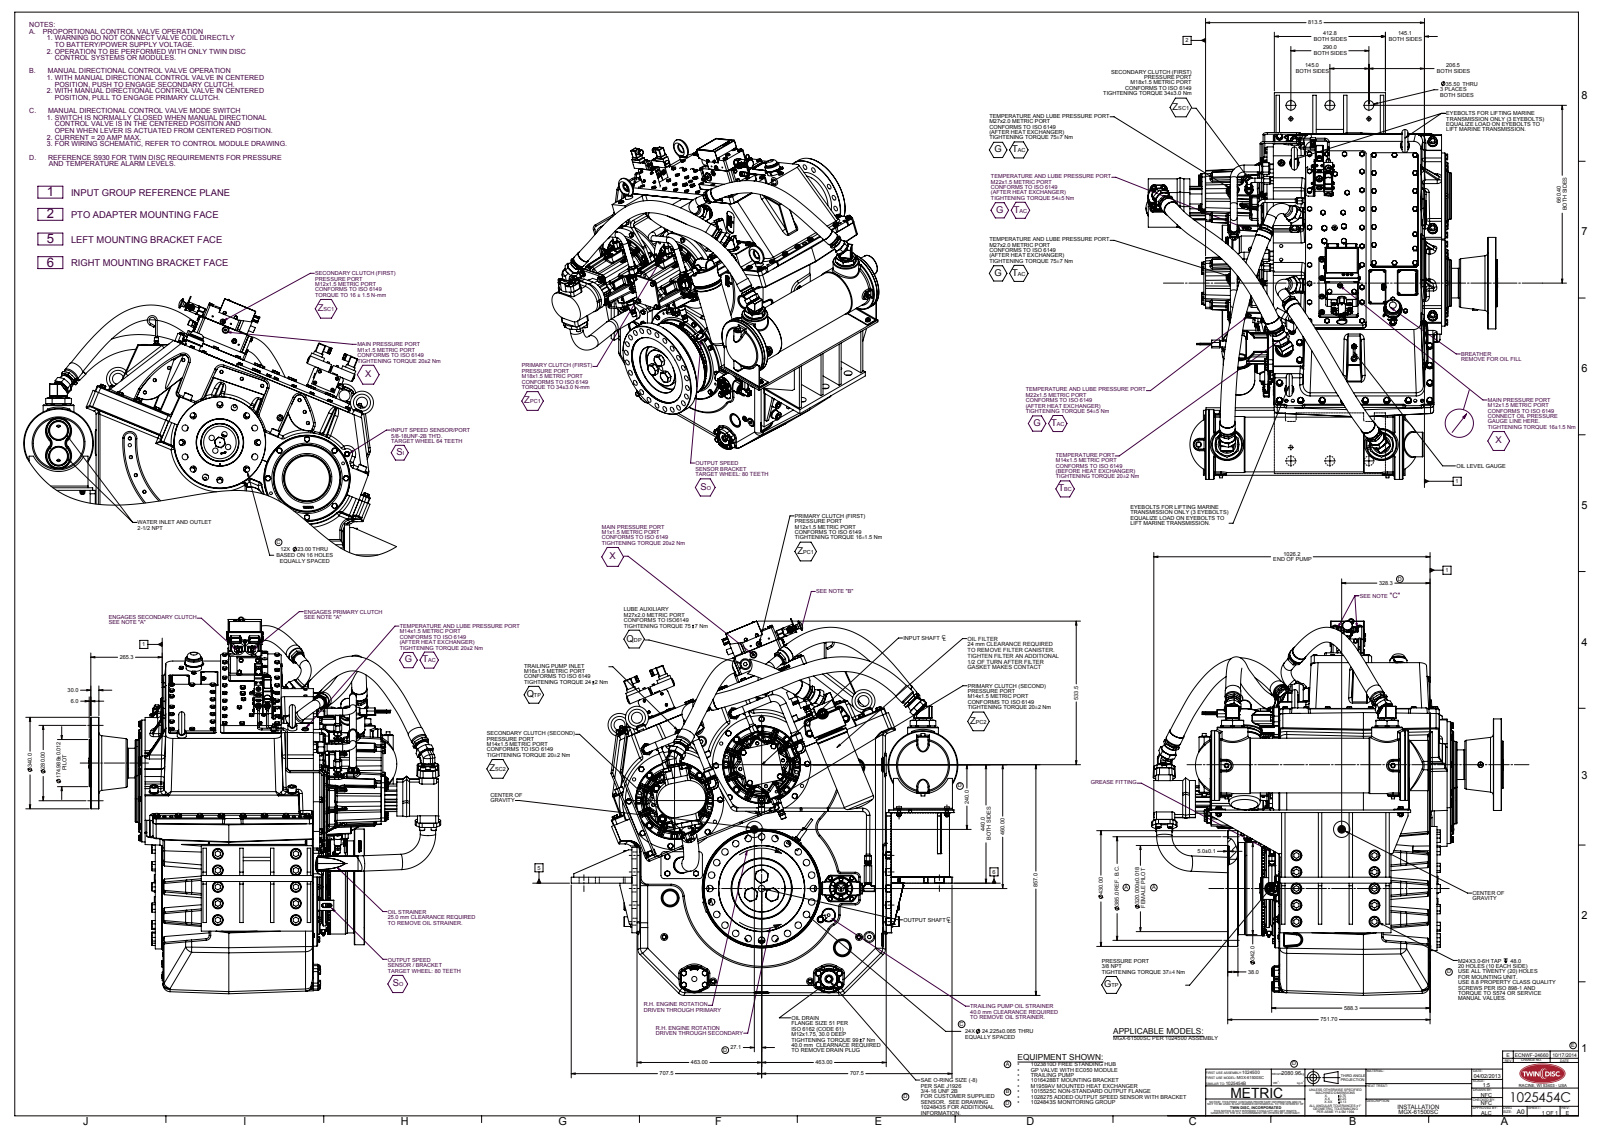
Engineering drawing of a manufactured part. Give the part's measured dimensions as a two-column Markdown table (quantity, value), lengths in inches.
| quantity | value |
| --- | --- |
| part name | 1025454C |
| STEP written by | SolidWorks 2010 (AUTOMOTIVE_DESIGN) |
| units | inches |
| bodies | 0 solids, 10051 faces (3178 planar, 4202 cylindrical, 2671 other) |
| overall size | 56.557 × 55.106 × 51.422 |
| round holes (diameter × count) | 0.472 × 39, 0.954 × 24, 0.906 × 13, 0.118 × 10, 0.402 × 10, 1.004 × 10, 0.787 × 8, 0.504 × 6, 1.398 × 6, 0.501 × 4, 0.571 × 4, 0.781 × 4 |
| round bosses / shafts (diameter × count) | 0.945 × 33, 0.25 × 20, 0.709 × 15, 1.417 × 10, 0.75 × 10, 1.575 × 7, 1.47 × 7, 0.669 × 7 |
| partial cylindrical surfaces (radius × count) | 1.35 × 192, 3.198 × 174, 0.236 × 156, 0.472 × 134, 0.118 × 115, 2.28 × 96, 0.045 × 90, 2.415 × 45 |
| main face-to-face distances | 0.75, 37.207, 0.118, 0.5, 21.988, 4.398, 36.457, 0.375, 21.87, 9.447 |
| hole center spacings | 11.417, 0.394, 2.421, 11.671, 0.787, 4.508, 4.843, 12.402 |
